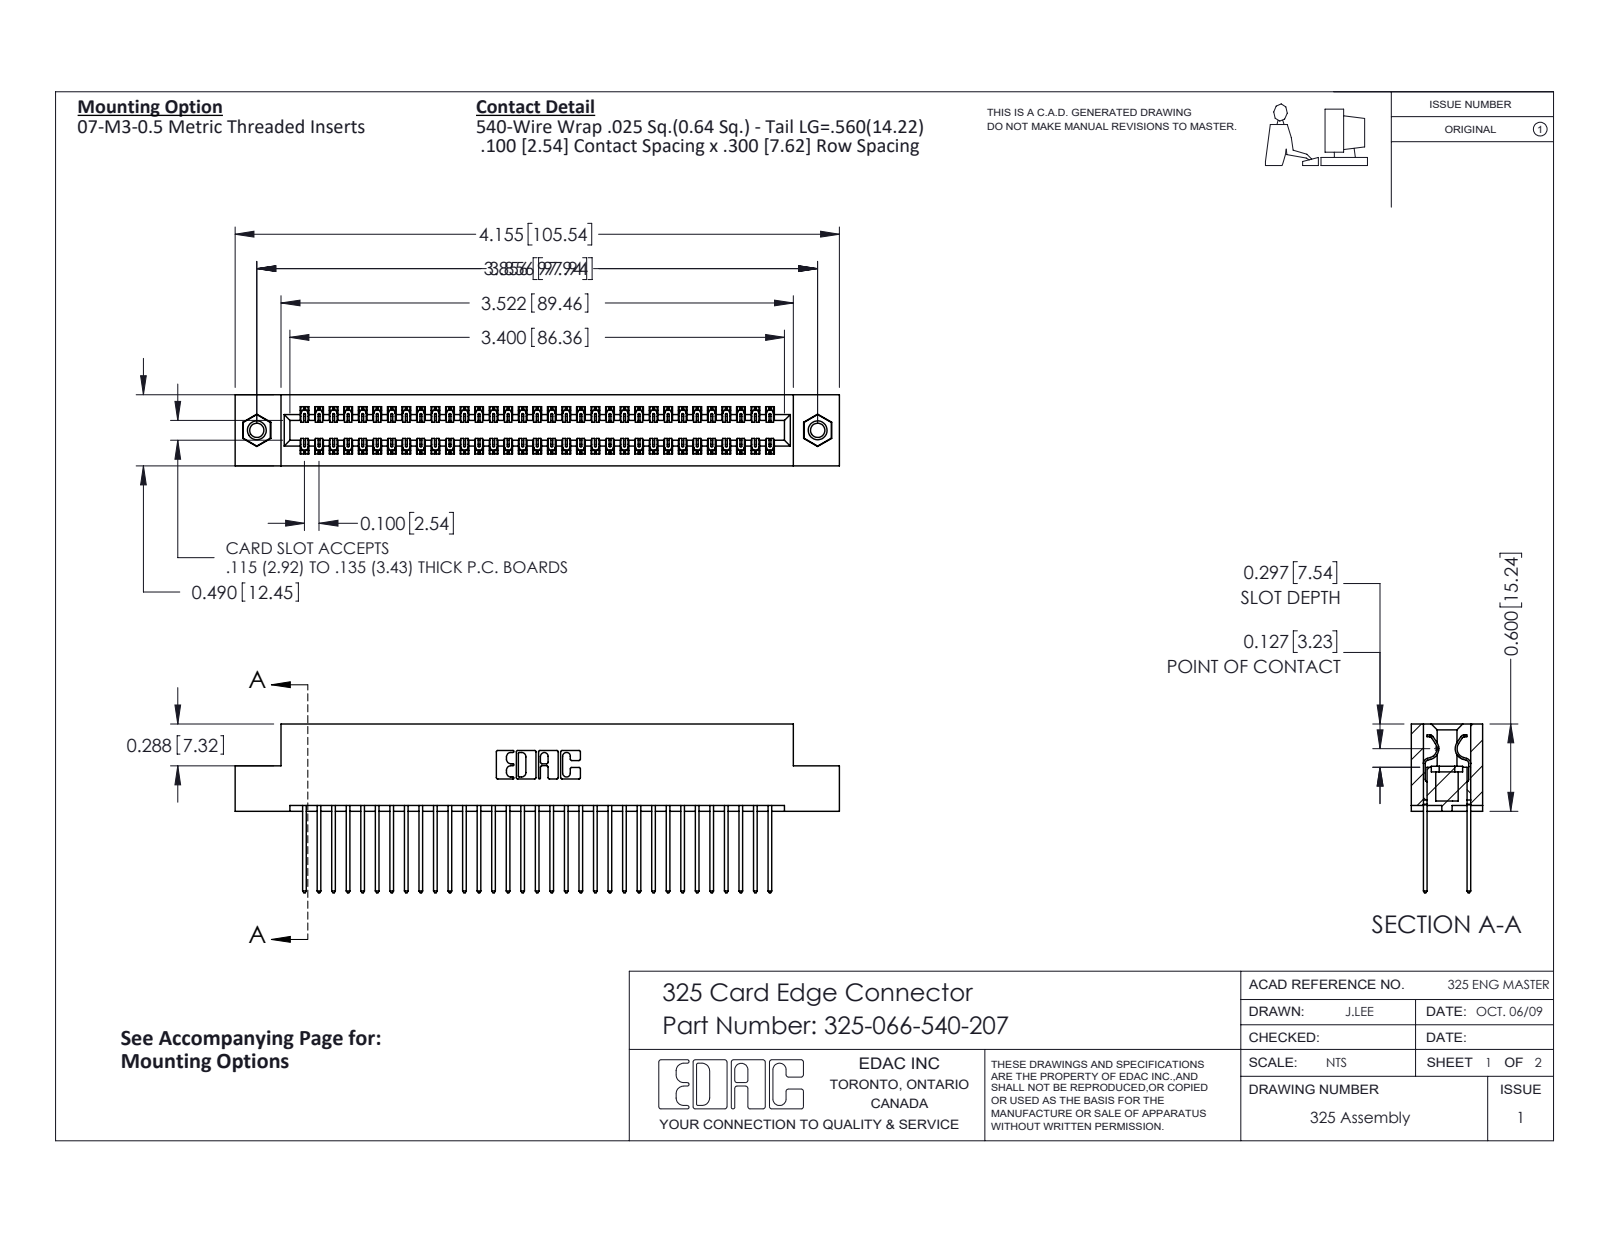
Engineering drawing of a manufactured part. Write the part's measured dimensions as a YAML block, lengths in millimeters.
part_name: "325-292-001_325-293-140; 325 Part_TI; 345-250-001_345-250-005-103; 325-066-540-207"
step_written_by: "SolidWorks 2016 (CONFIG_CONTROL_DESIGN)"
units: millimeters
bodies: {solids: 69, faces: 3606, planar: 2478, cylindrical: 1112, other: 16}
overall_size: [105.5, 29.5, 12.4]
volume: 13800
surface_area: 17680
round_holes:
  - {diameter: 2.5, count: 2}
  - {diameter: 3.2, count: 2}
  - {diameter: 4.1, count: 2}
round_bosses_or_shafts:
  - {diameter: 3.9, count: 2}
partial_cylinders:
  - {radius: 0.2, count: 99}
  - {radius: 0.3, count: 66}
  - {radius: 0.3, count: 22}
  - {radius: 0.2, count: 6}
  - {radius: 0.8, count: 6}
  - {radius: 0.7, count: 3}
  - {radius: 0.4, count: 2}
  - {radius: 0.6, count: 2}
face_to_face_distances: [2.1, 10.3, 7.6, 2.7, 9.7, 0.6, 12.4, 8.3, 7, 14.2]
hole_center_spacings: [97.9]
